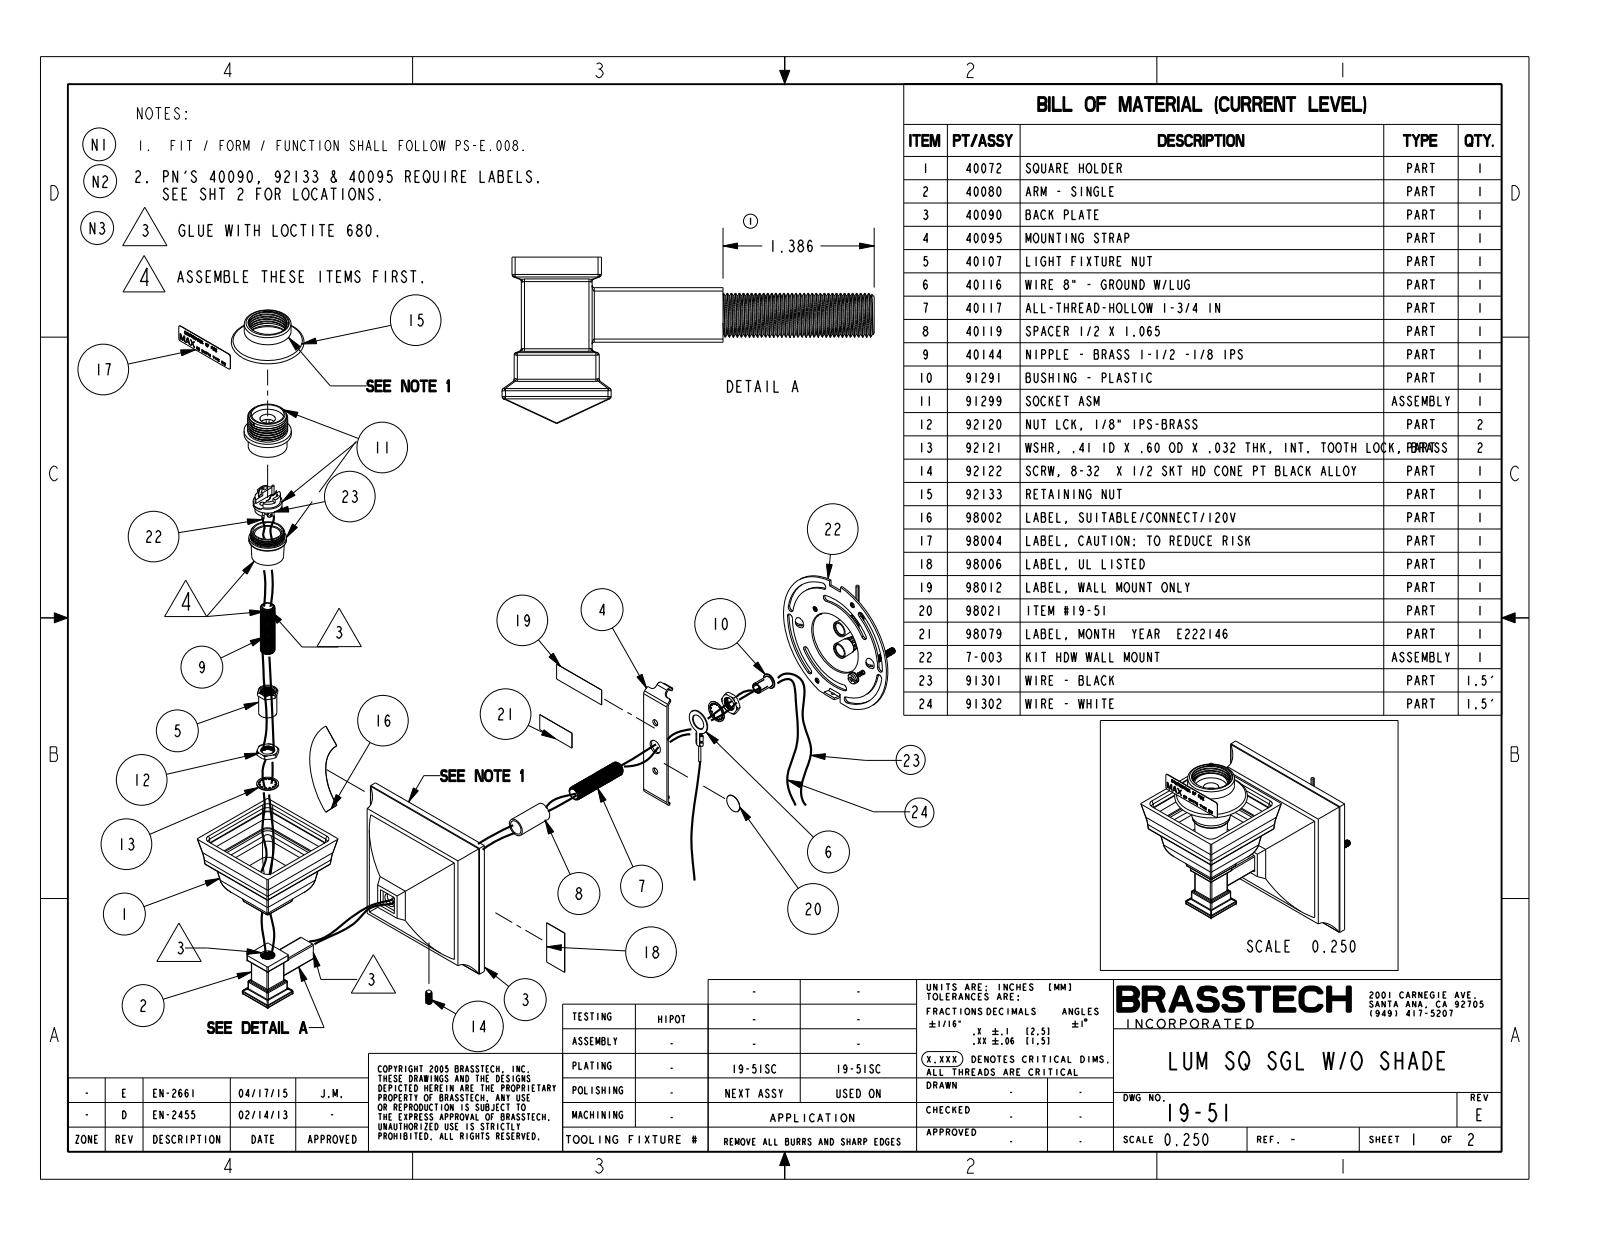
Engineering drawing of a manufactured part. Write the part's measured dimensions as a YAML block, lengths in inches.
part_name: "19-51SC_SW0001"
step_written_by: "PRO/ENGINEER BY PARAMETRIC TECHNOLOGY CORPORATION, 2009300 (CONFIG_CONTROL_DESIGN)"
units: inches
bodies: {solids: 0, faces: 375, planar: 91, cylindrical: 156, other: 128}
overall_size: [8.816, 5.421, 4.41]
round_holes:
  - {diameter: 0.13, count: 1}
partial_cylinders:
  - {radius: 0.03, count: 62}
  - {radius: 0.025, count: 28}
  - {radius: 0.062, count: 12}
  - {radius: 0.06, count: 8}
  - {radius: 0.017, count: 4}
  - {radius: 0.02, count: 4}
  - {radius: 0.5, count: 4}
  - {radius: 0.75, count: 4}
face_to_face_distances: [0.674, 4.1, 2.53, 1.866, 2.366, 1.867, 2.367, 0.5, 2.1, 6.2]
